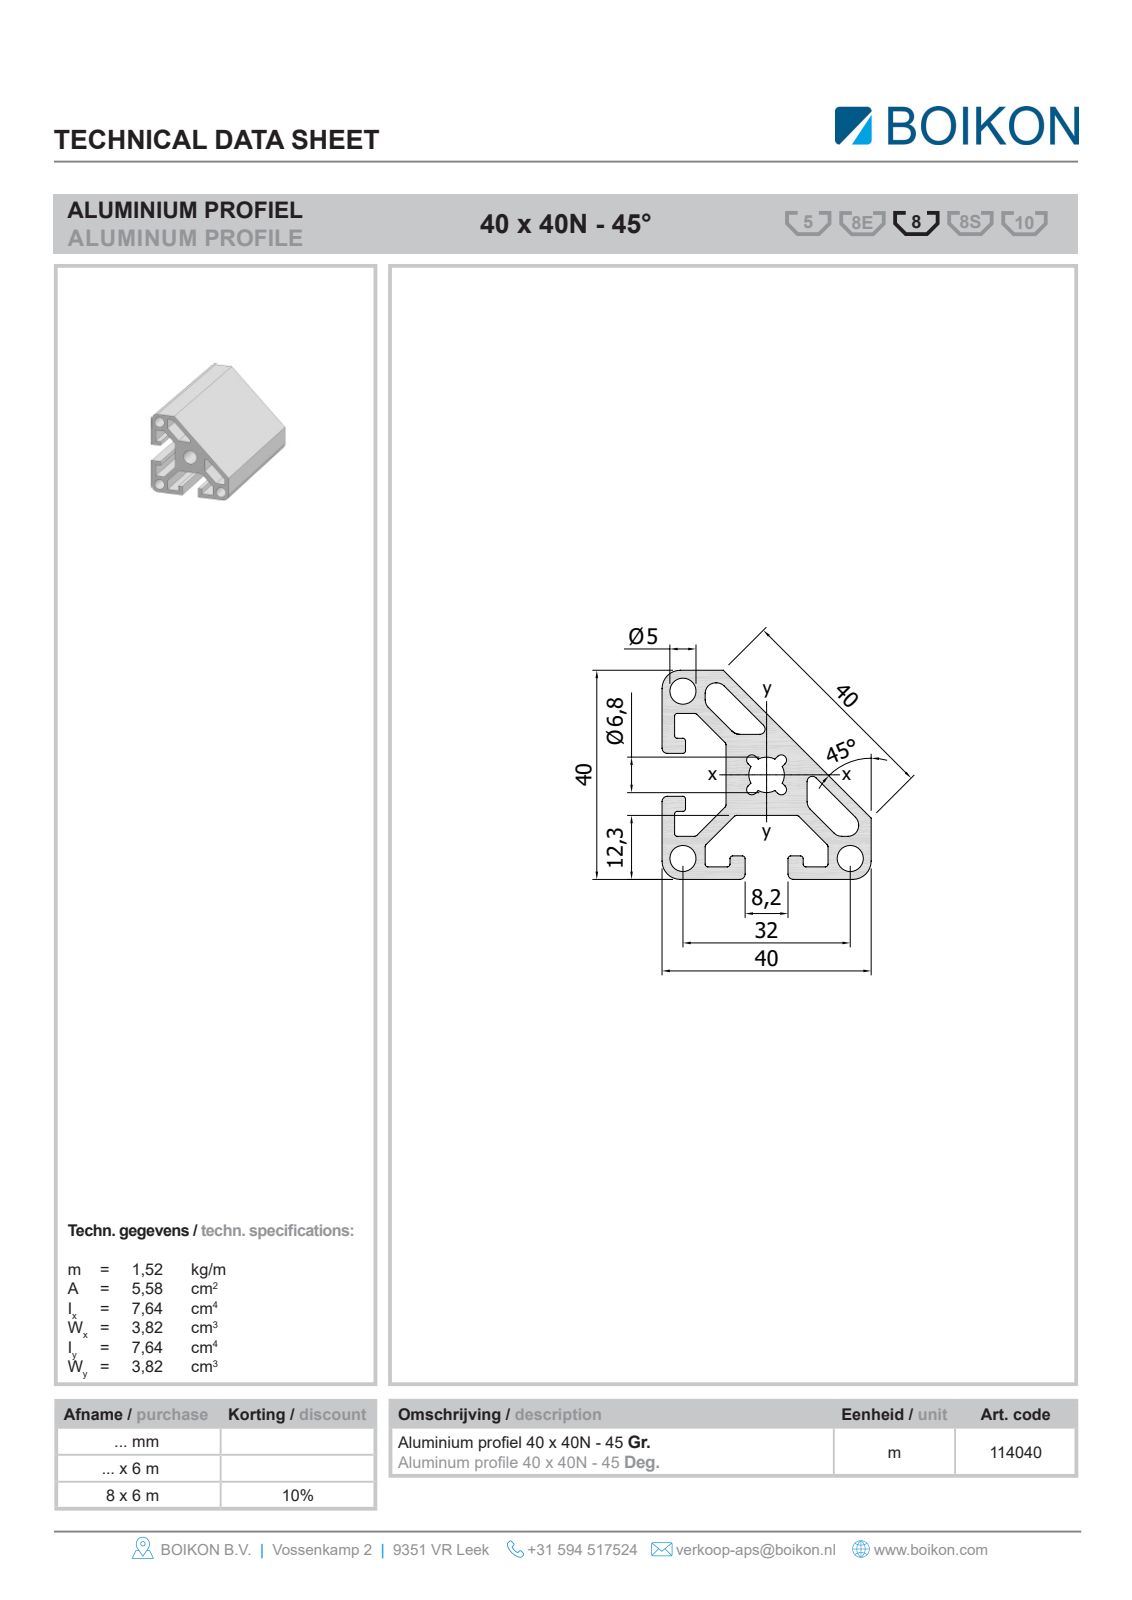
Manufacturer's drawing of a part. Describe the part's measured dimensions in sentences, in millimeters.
The part is named "Root; 11404040x40N-45BOIKON0". Its 3-D file was written by "HiCAD 2013 1802.4 Build 509 (AUTOMOTIVE_DESIGN)". It is 1 solid with 54 faces: 47 planar, 7 cylindrical and 0 other. Overall it measures 1000 by 40 by 40 millimeters. Its volume is 546 402 cubic millimeters and its surface area 396 400 square millimeters. Round holes: 3 of diameter 5, 1 of diameter 6.8. Partial cylindrical surfaces (rounded edges, fillets, slot ends): 3 of radius 3. The main face-to-face distances are 2, 12.25, 2.5, 27.75, 24.1, 10.25, 8.25, 4, 31.75, 13.9. The hole center spacings are 22.63, 32, 45.25.
